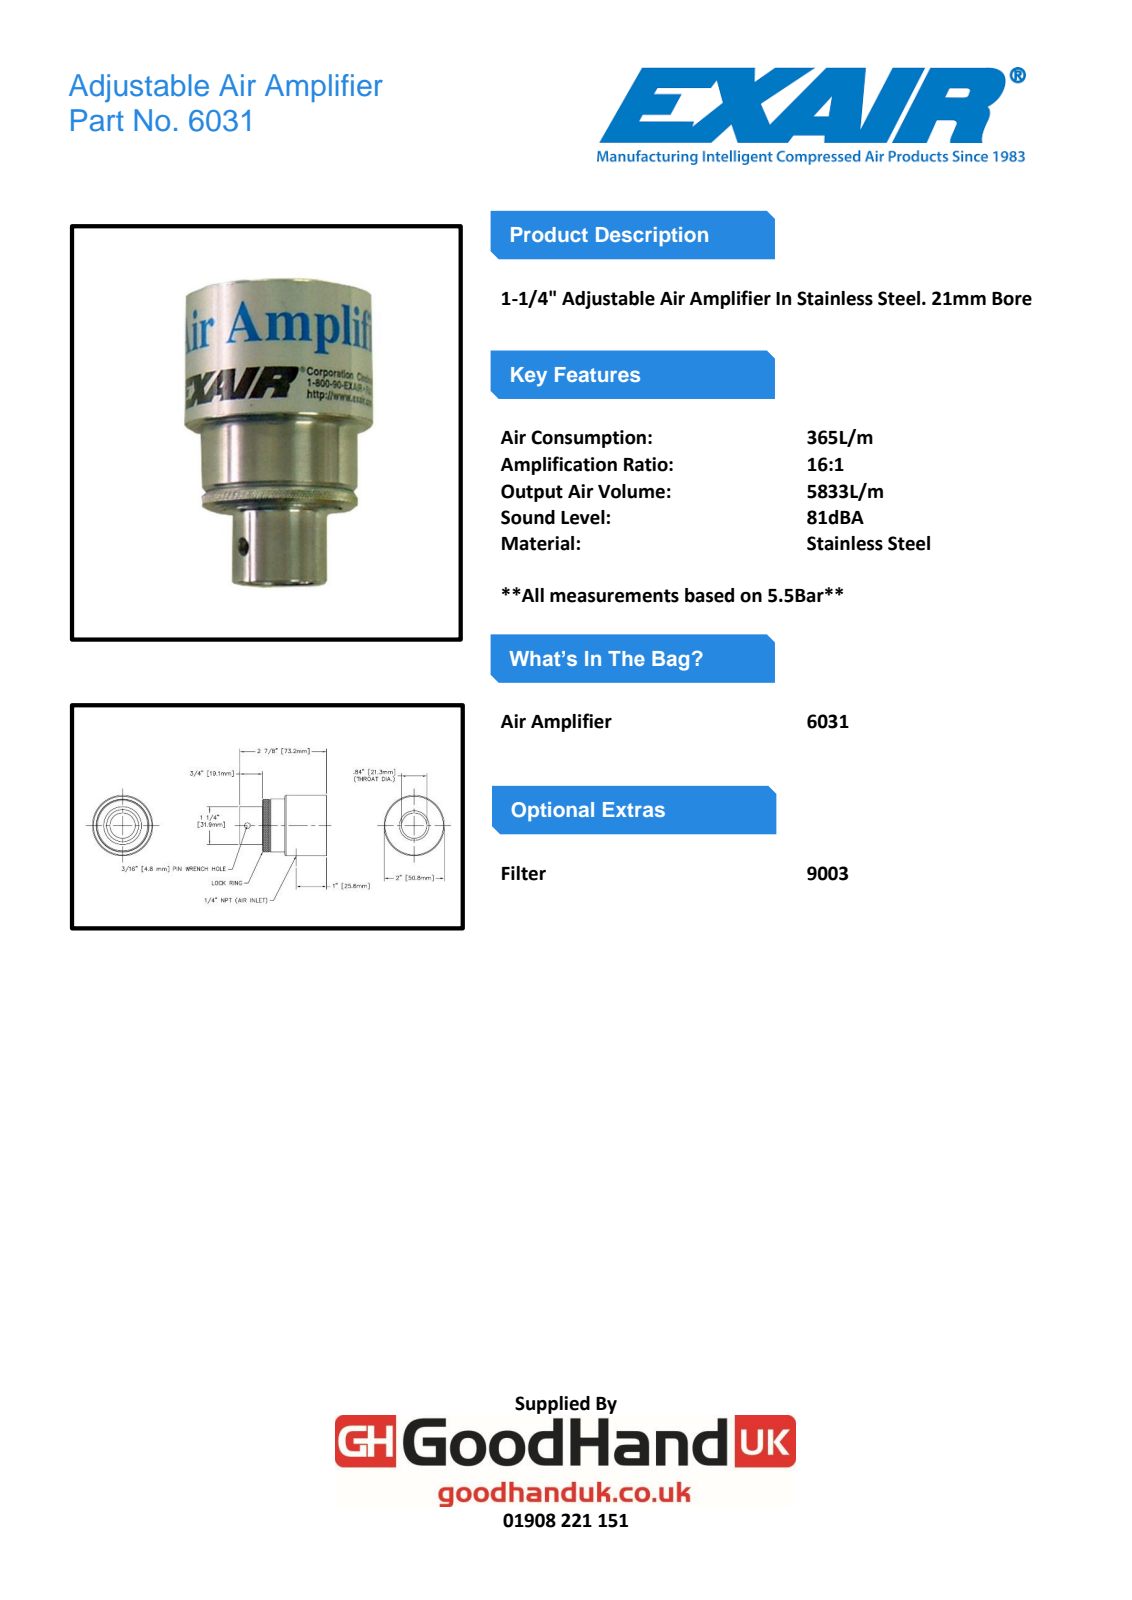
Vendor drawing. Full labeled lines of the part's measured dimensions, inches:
STEP written by: Autodesk Inventor 2010 (AUTOMOTIVE_DESIGN)
Units: inches
Bodies: 3 solids, 33 faces (9 planar, 10 cylindrical, 14 other)
Overall size (bounding box): 2.881 × 2 × 2
Volume: 4.459 in³ · Surface area: 44.76 in²
Round holes (diameter × count): ⌀0.186 ×1, ⌀1.376 ×1, ⌀1.396 ×1
Round bosses / shafts (diameter × count): ⌀2 ×1, ⌀1.75 ×1, ⌀1.734 ×1, ⌀1.438 ×1, ⌀1.366 ×1, ⌀1.256 ×1
Main face-to-face distances: 0.75, 1.25, 1.5, 0.5, 0.25, 1, 2.25, 1.375, 0.625, 0.375
